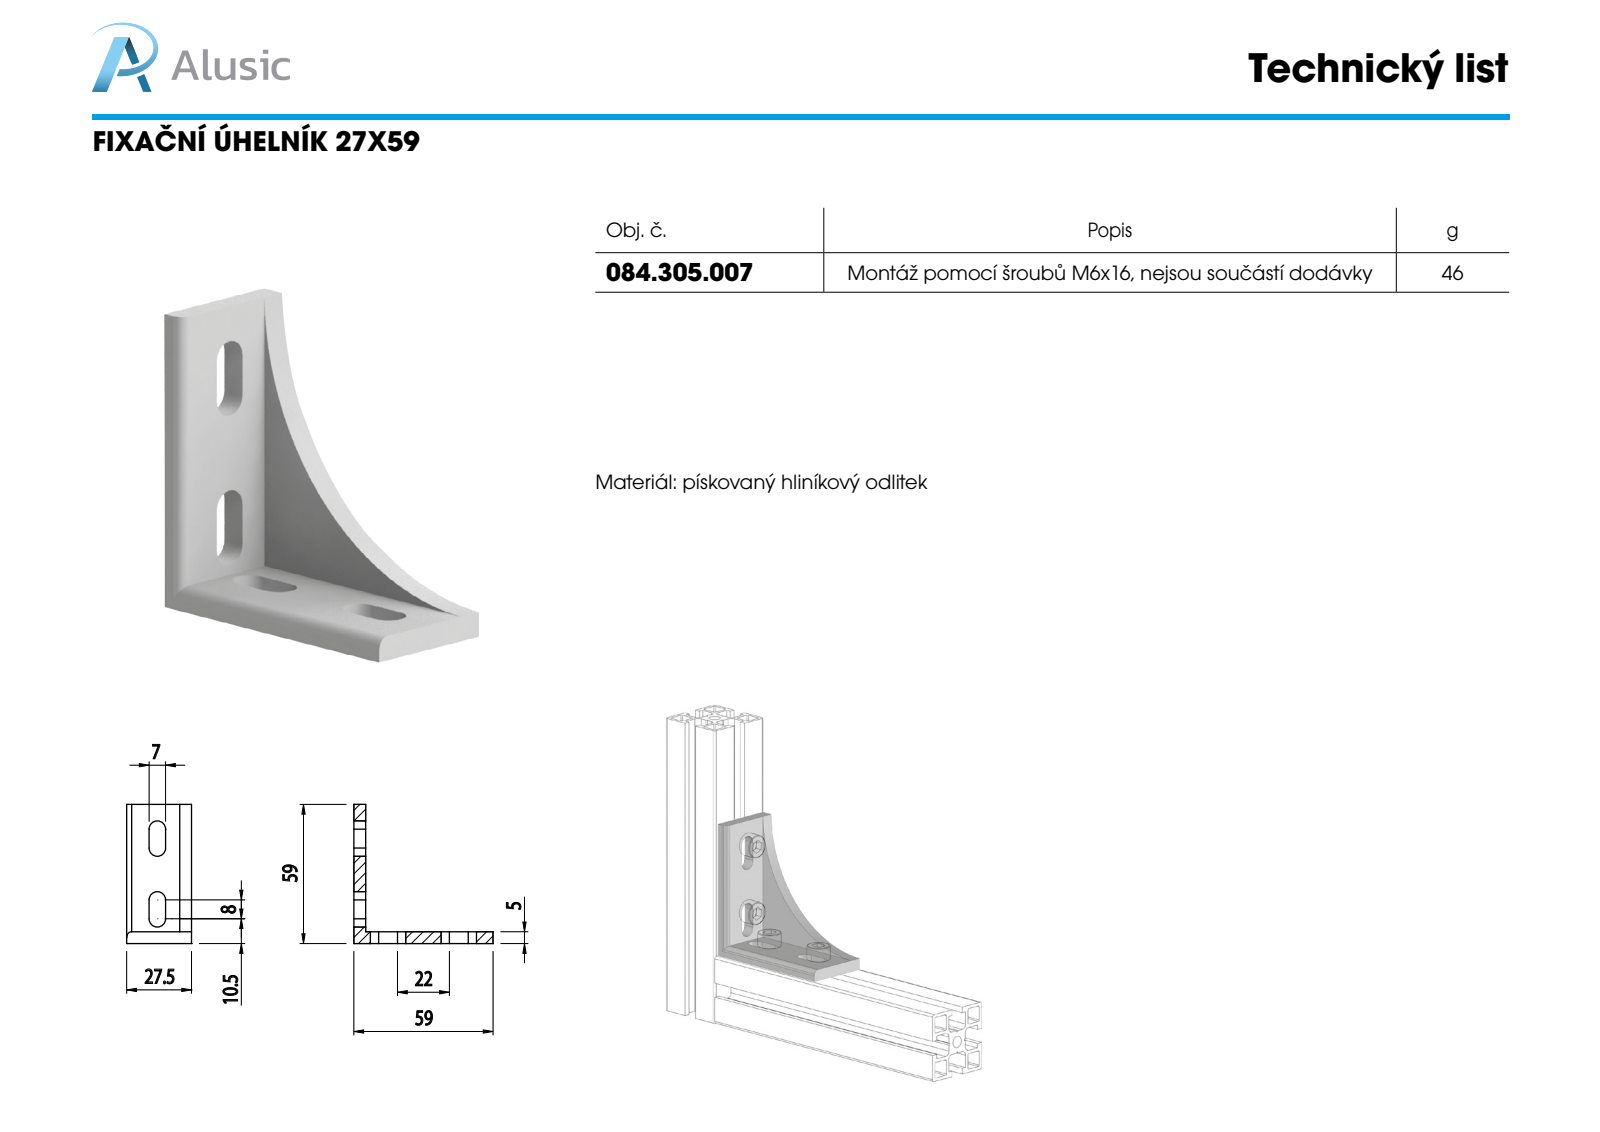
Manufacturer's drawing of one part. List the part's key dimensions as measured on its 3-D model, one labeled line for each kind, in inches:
Part name (STEP PRODUCT): 084.305.007
STEP written by: SolidWorks 2011 (CONFIG_CONTROL_DESIGN)
Units: inches
Bodies: 1 solid, 26 faces (17 planar, 9 cylindrical, 0 other)
Overall size (bounding box): 2.323 × 2.323 × 1.083
Volume: 1.018 in³ · Surface area: 13.46 in²
Partial cylindrical surfaces — rounded edges, fillets, slot ends (radius × count): R0.144 ×8, R2.126 ×1
Main face-to-face distances: 0.197, 0.217, 1.083, 0.866, 2.323, 2.126, 0.715, 0.498, 0.368, 0.427
